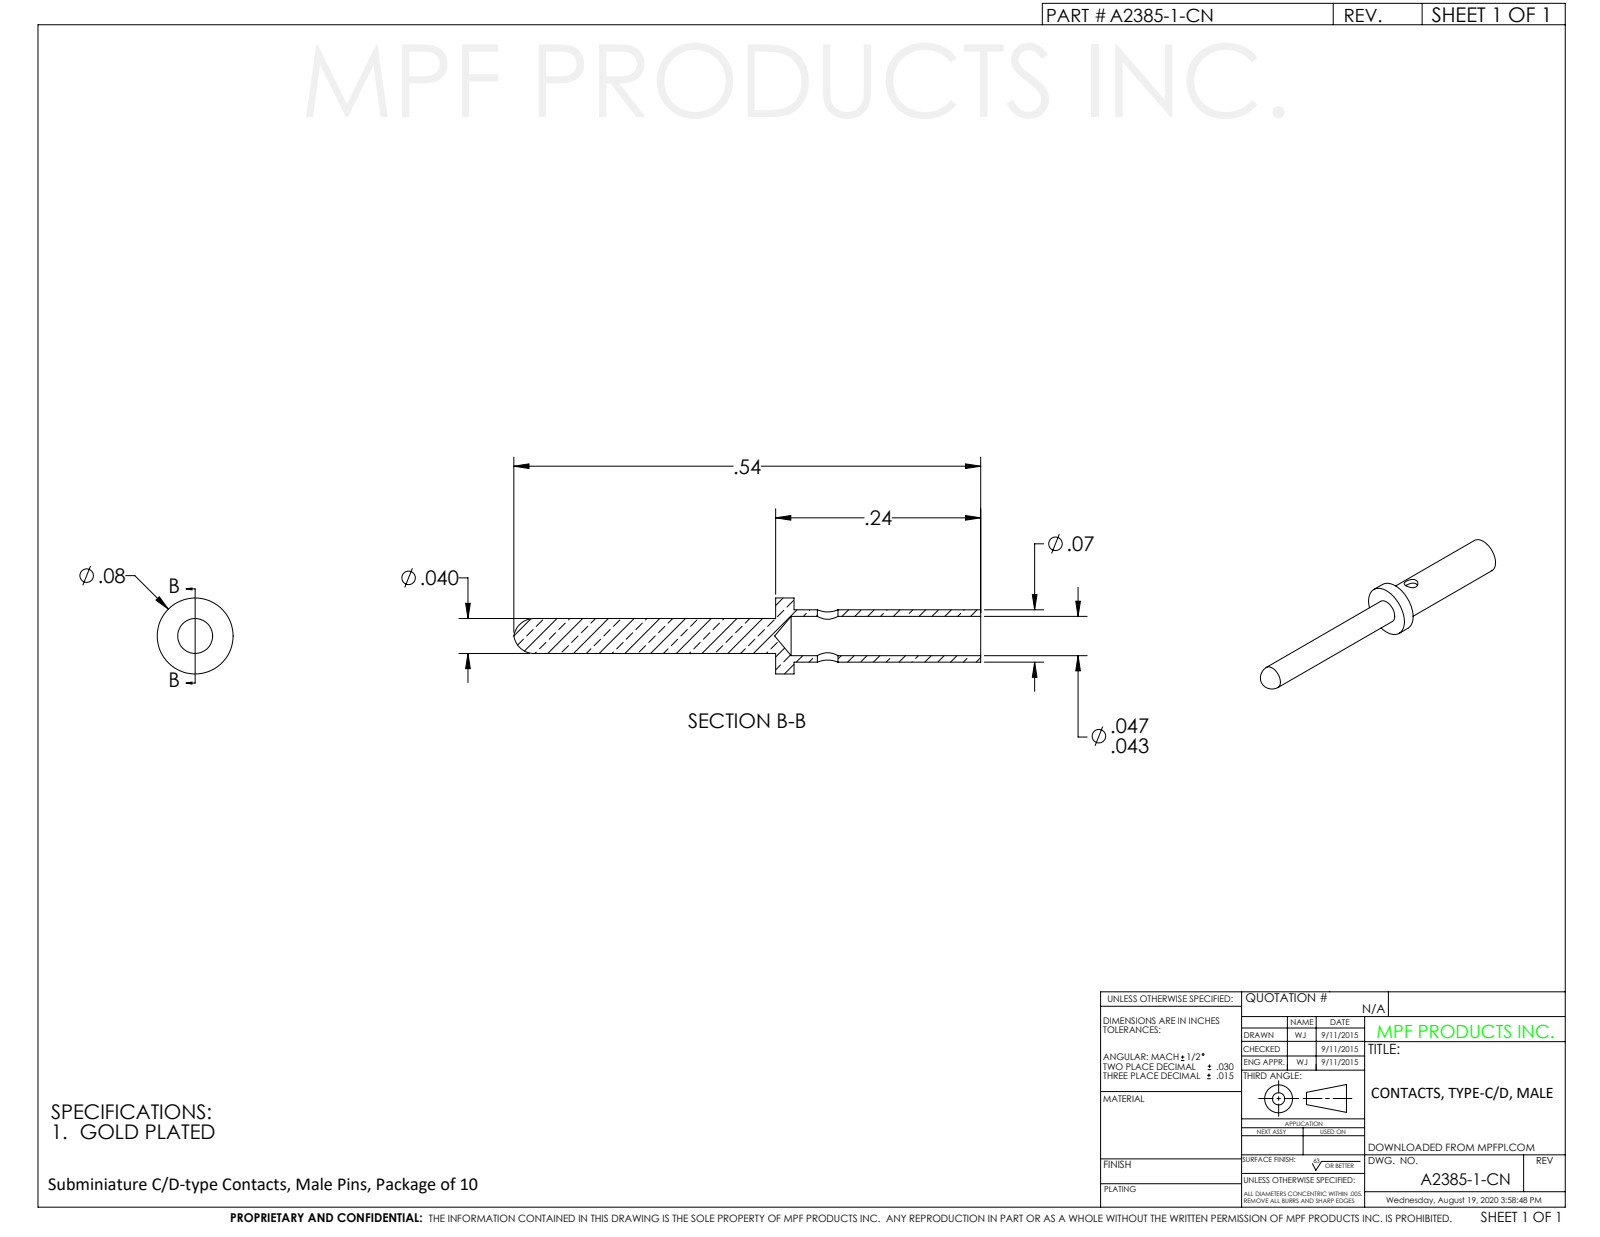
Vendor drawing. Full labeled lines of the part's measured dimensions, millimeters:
Part name (STEP PRODUCT): A2385-1-CN
STEP written by: SolidWorks 2012 (CONFIG_CONTROL_DESIGN)
Units: millimetres
Bodies: 1 solid, 19 faces (3 planar, 12 cylindrical, 4 other)
Overall size (bounding box): 13.6 × 2.2 × 2.2
Volume: 20 mm³ · Surface area: 81 mm²
Round holes (diameter × count): ⌀0.6 ×1, ⌀1.1 ×1
Round bosses / shafts (diameter × count): ⌀2.2 ×1, ⌀1.5 ×1, ⌀1 ×1
Main face-to-face distances: 0.5, 5.4, 6
